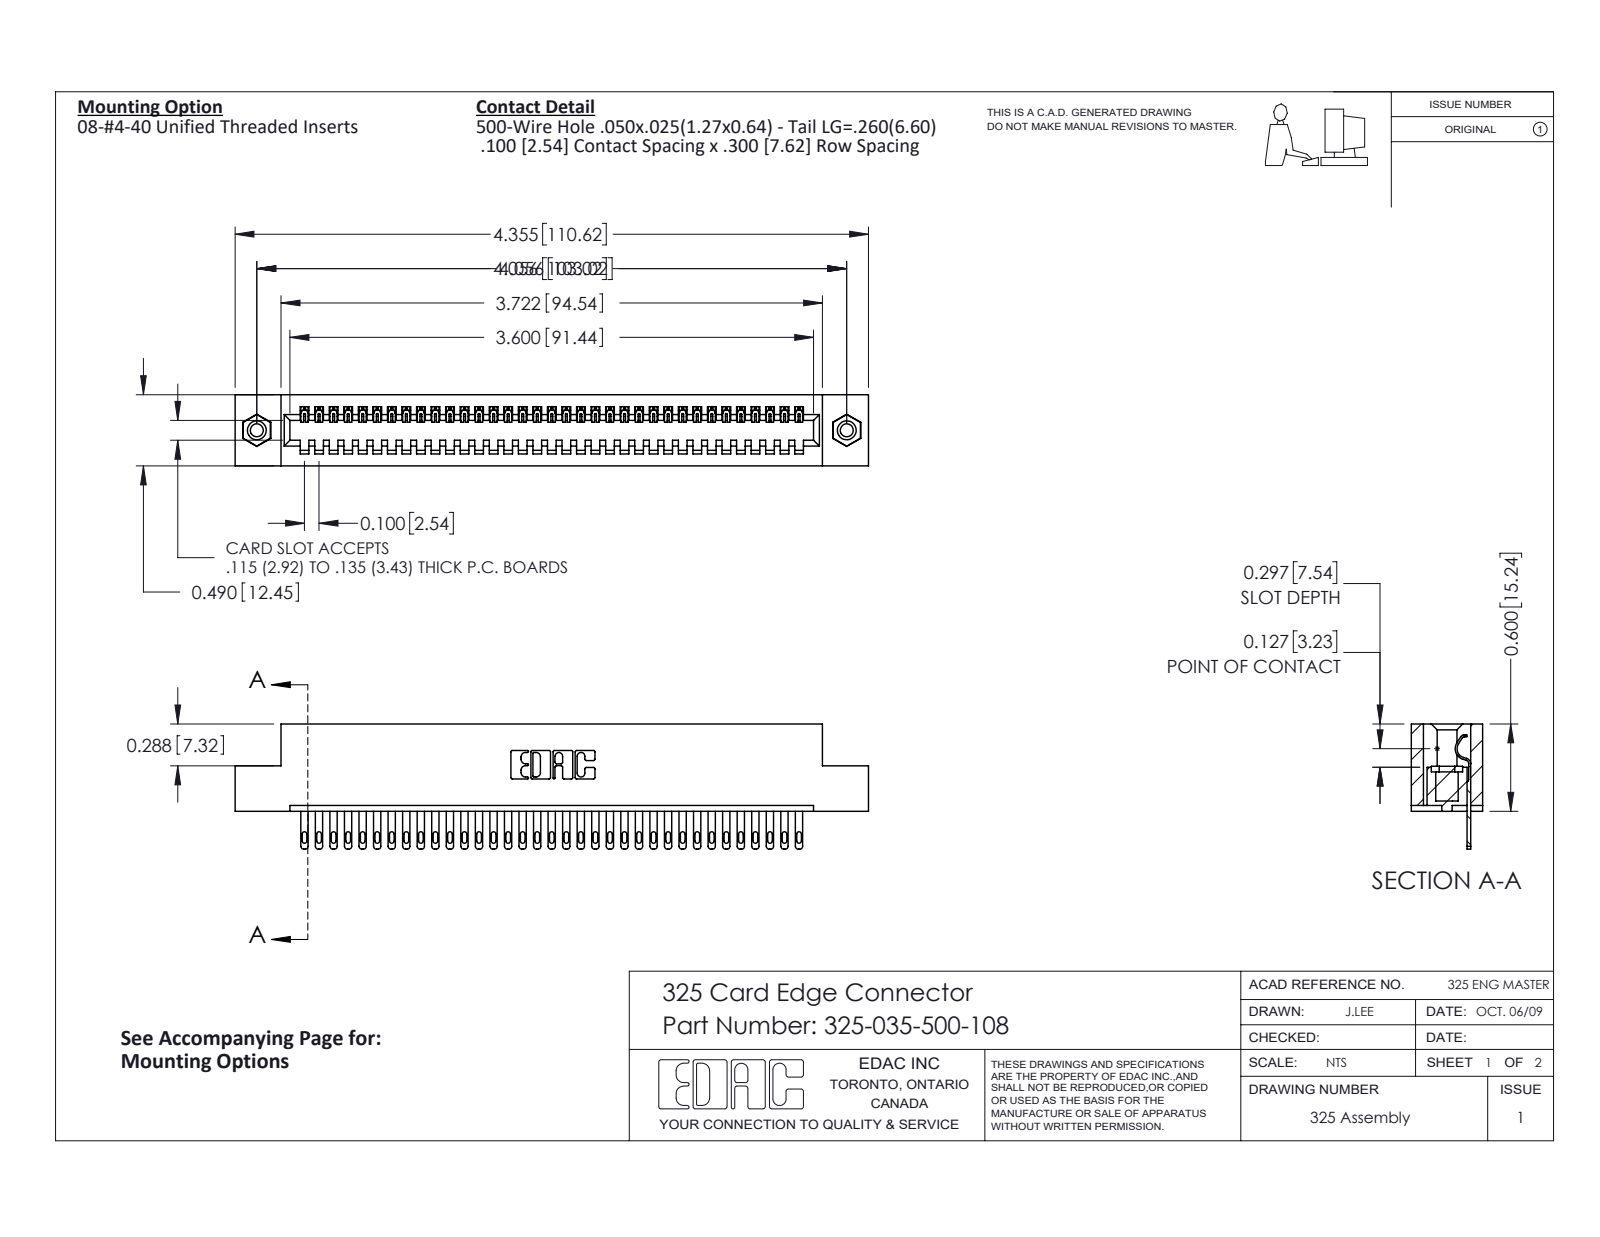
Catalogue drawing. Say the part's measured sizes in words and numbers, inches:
The part is named "325-035-500-108; 325-292-001_325-293-100; 325 Part_TI; 345-250-001_345-250-003-102". Its 3-D file was written by "SolidWorks 2016 (CONFIG_CONTROL_DESIGN)". It is 38 solids with 2064 faces: 1362 planar, 686 cylindrical and 16 other. Overall it measures 4.355 by 0.86 by 0.49 inches. Its volume is 0.855 cubic inches and its surface area 23.68 square inches. Round holes: 2 of diameter 0.089, 2 of diameter 0.125, 2 of diameter 0.16. Round bosses or shafts: 2 of diameter 0.155. Partial cylindrical surfaces (rounded edges, fillets, slot ends): 70 of radius 0.006, 70 of radius 0.016, 70 of radius 0.02, 22 of radius 0.01, 6 of radius 0.007, 6 of radius 0.031, 3 of radius 0.026, 1 of radius 0.014. The main face-to-face distances are 0.083, 0.407, 0.49, 0.3, 0.107, 0.383, 0.025, 0.325, 0.56, 0.04. The hole center spacings are 4.056.
